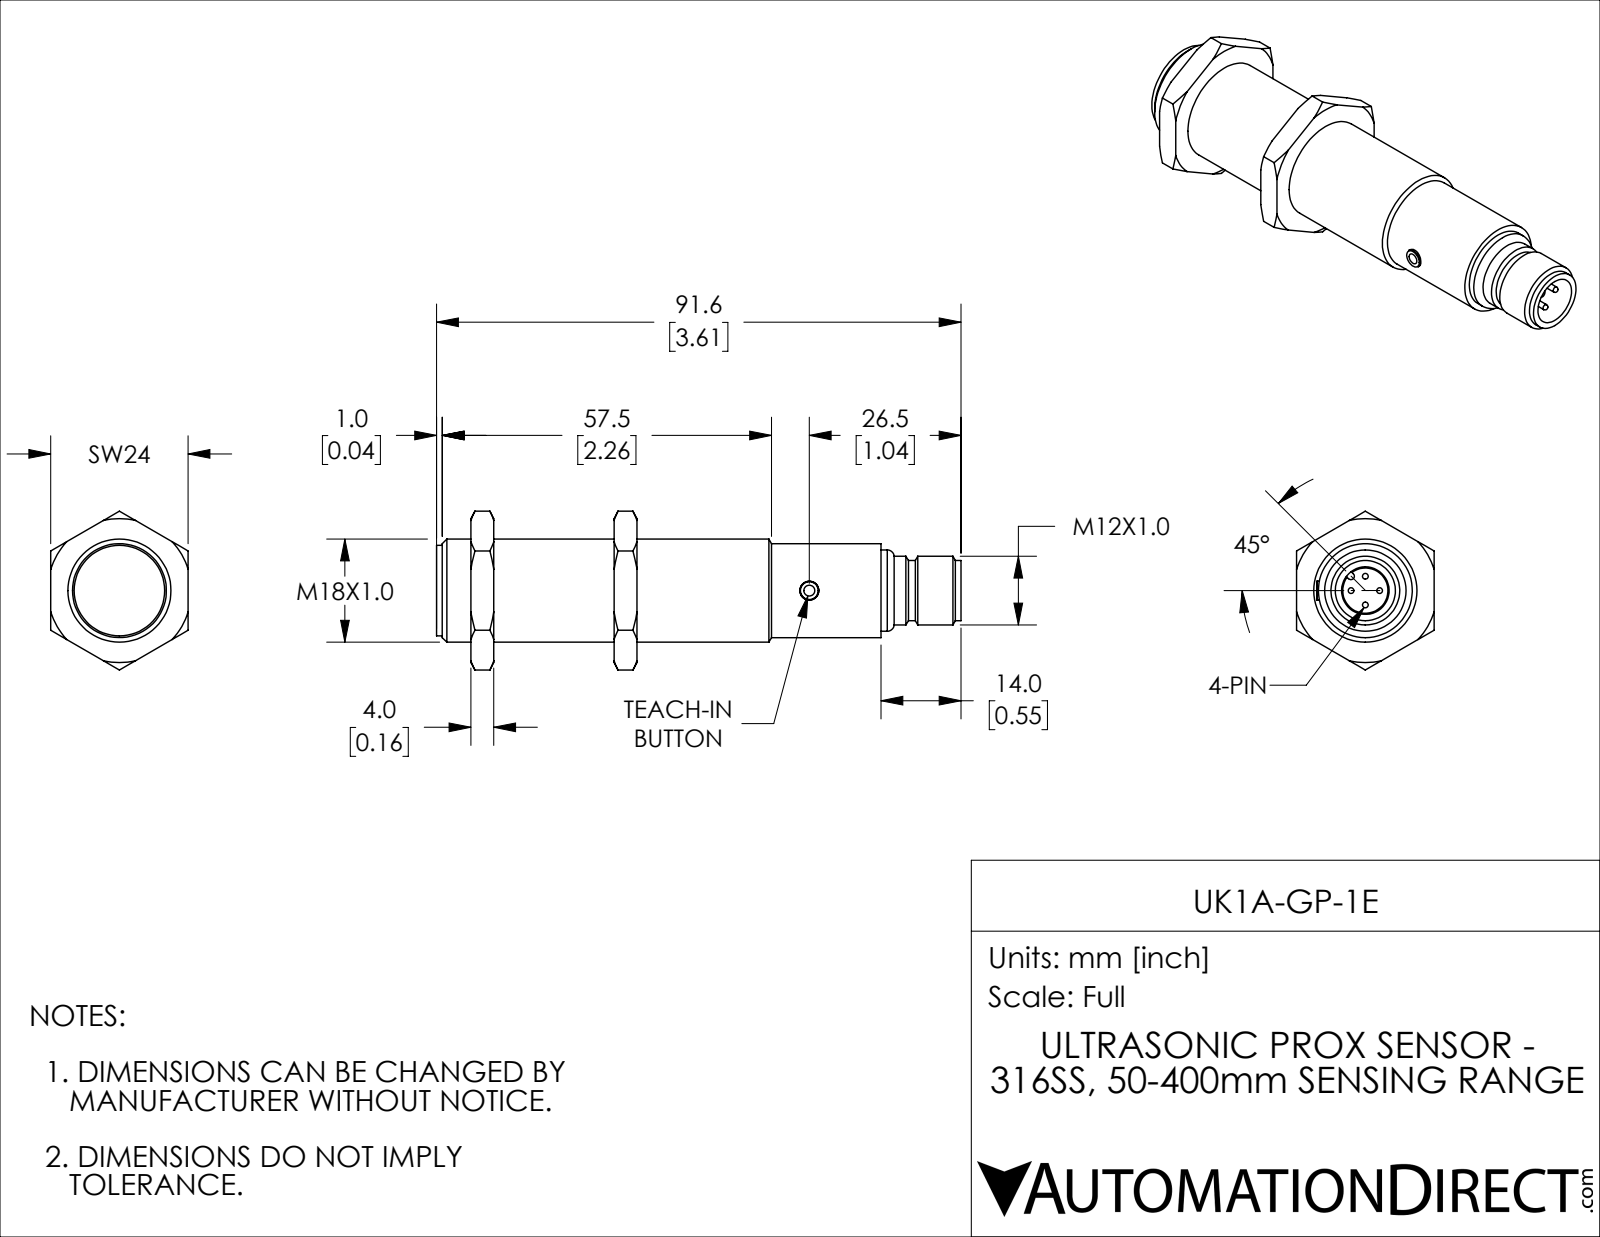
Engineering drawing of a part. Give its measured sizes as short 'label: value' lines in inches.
name: UK1A-GP-1E
written by: SolidWorks 2018 (AUTOMOTIVE_DESIGN)
unit: in
bodies: 4 solids, 113 faces (27 planar, 35 cylindrical, 51 other)
size: 3.606 × 1.091 × 0.945
volume: 1.338 in³; area: 11.97 in²
holes: 1× ⌀0.13, 1× ⌀0.327, 1× ⌀0.709
bosses: 4× ⌀0.039, 1× ⌀0.646, 1× ⌀0.622, 1× ⌀0.559, 1× ⌀0.472, 1× ⌀0.413
rounds: 1× R0.024
face distances: 0.984, 0.157, 0.945, 1.142, 0.827, 0.236, 0.394, 1.22, 1.378, 3.055
